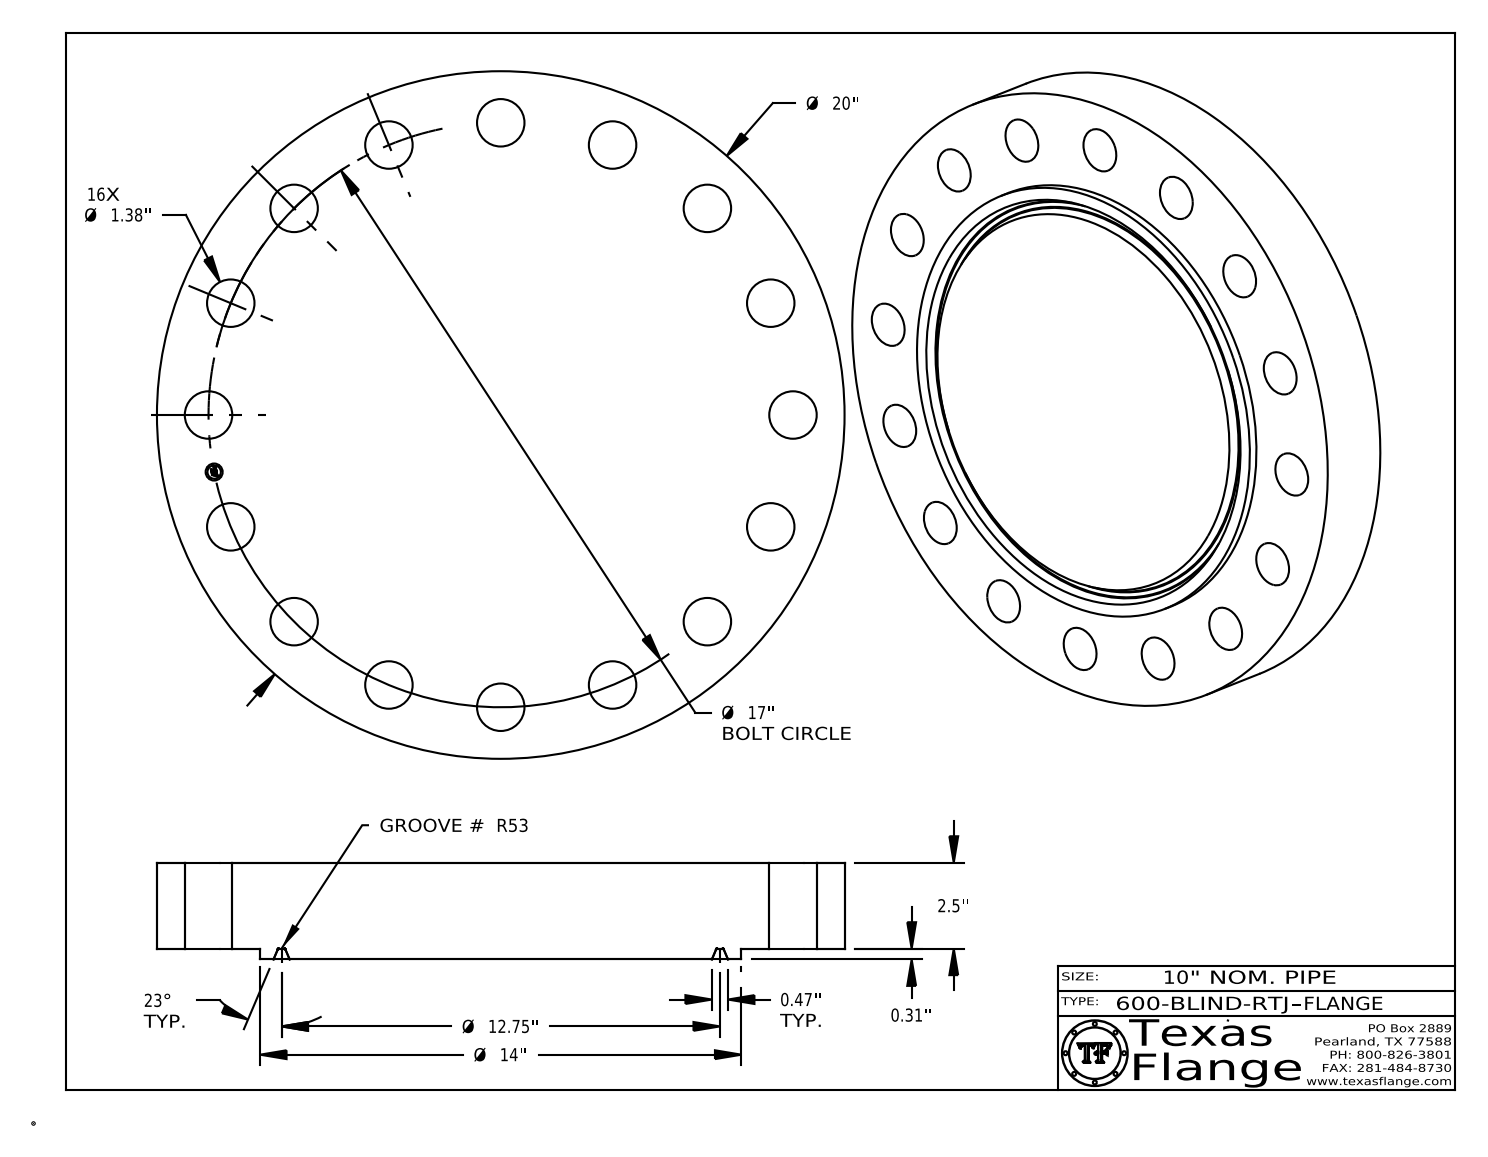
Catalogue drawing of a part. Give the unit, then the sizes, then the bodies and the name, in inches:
Units: inches
Overall size (bounding box): 20 × 20 × 2.813
Round holes (diameter × count): ⌀1.38 ×16, ⌀0.495 ×1
Round bosses / shafts (diameter × count): ⌀0.03 ×8, ⌀20 ×1, ⌀14 ×1, ⌀0.39 ×1
Main face-to-face distances: 2.5, 0.313, 2.813, 2.798, 2.485, 0.015, 0.148, 0.145, 0.027, 0.096
Hole centre spacings: 3.317, 14.135, 6.506, 12.021, 9.444, 9.445, 15.706, 15.706
Volume: 769.5 in³ · Surface area: 941 in²
Bodies: 1 solid, 434 faces (370 planar, 56 cylindrical, 8 other)
Part name (STEP PRODUCT): 600-BLIND-RTJ
STEP written by: CATIA V5 STEP AP214 (AUTOMOTIVE_DESIGN)
